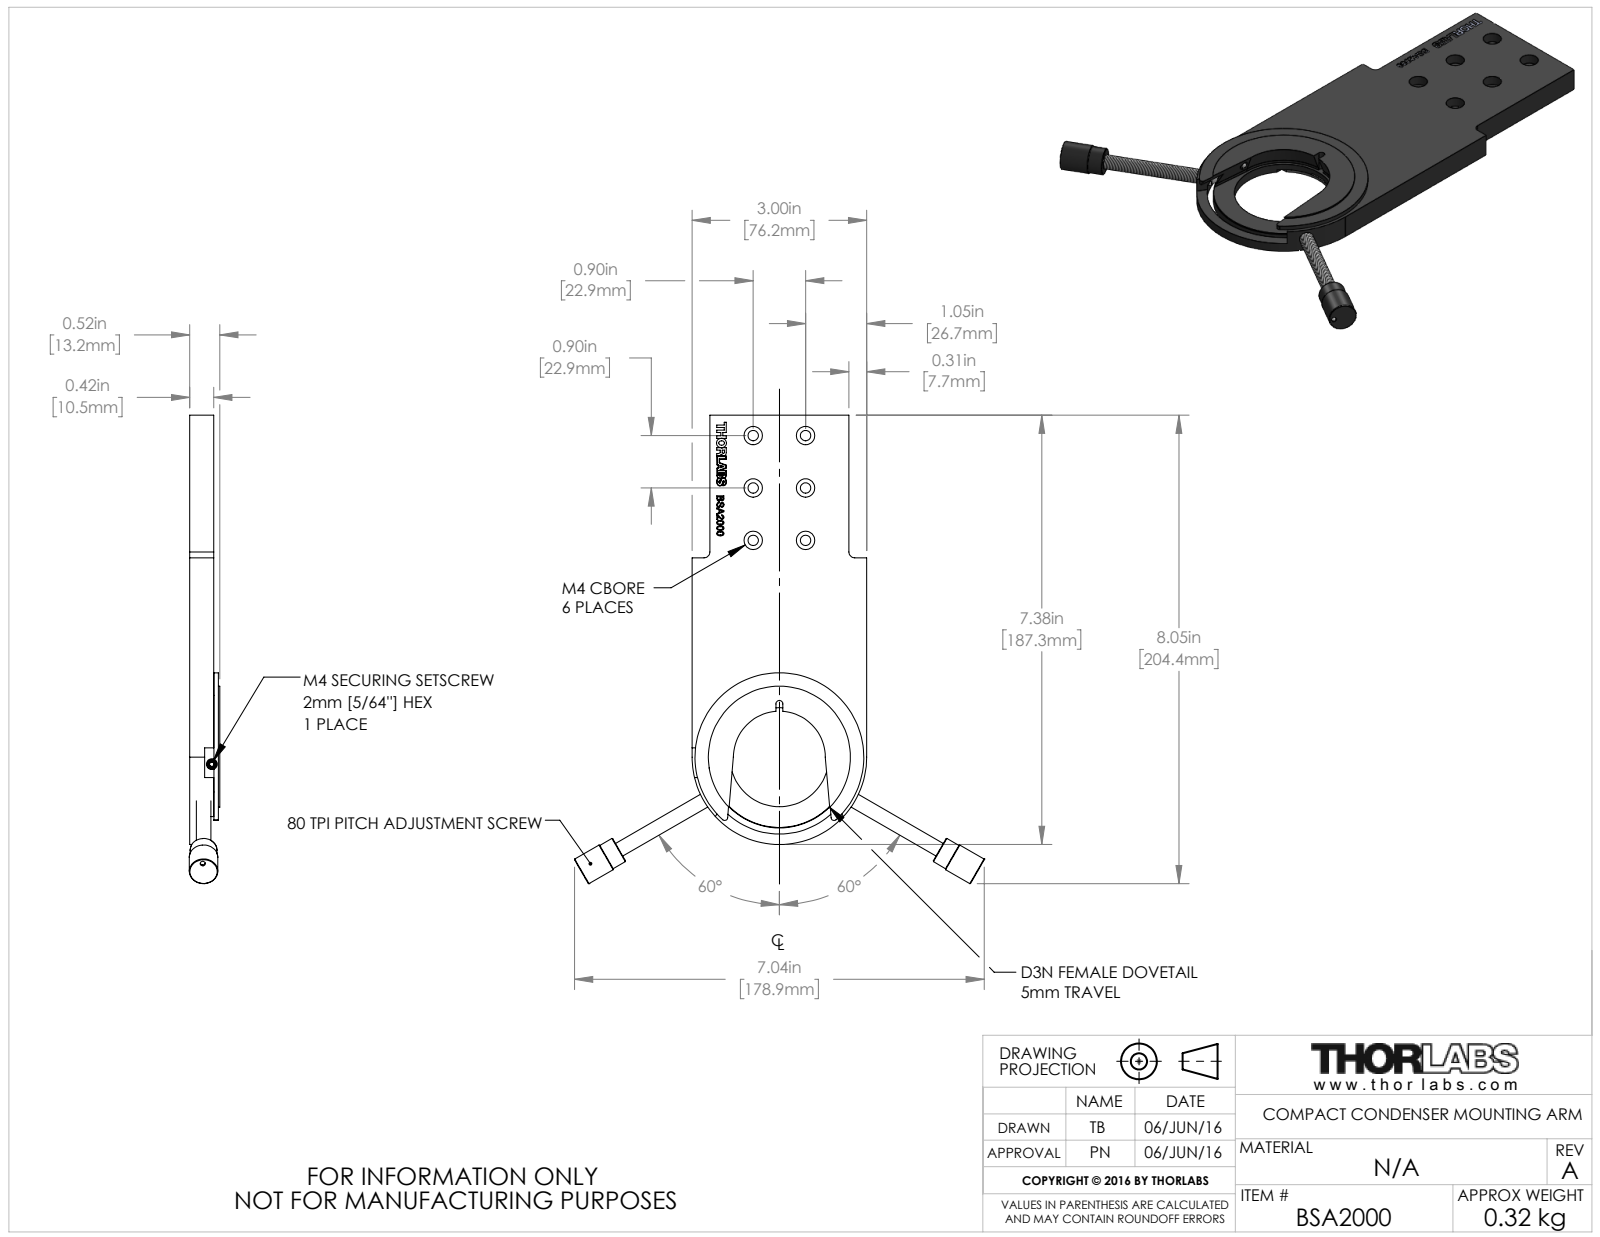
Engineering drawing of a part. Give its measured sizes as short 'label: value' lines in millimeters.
name: TTN030414-E0W
written by: SolidWorks 2016 (AUTOMOTIVE_DESIGN)
unit: mm
bodies: 17 solids, 753 faces (286 planar, 232 cylindrical, 235 other)
size: 204.4 × 178.88 × 13.34
volume: 108 611 mm³; area: 45 212 mm²
holes: 6× ⌀4.5, 6× ⌀8, 2× ⌀2.29, 2× ⌀2.5, 2× ⌀4.78, 2× ⌀5.94, 2× ⌀6.04, 2× ⌀6.3, 1× ⌀2.97, 1× ⌀3.3, 1× ⌀4.7, 1× ⌀43.18
bosses: 3× ⌀3, 2× ⌀12.45, 2× ⌀11.68, 2× ⌀6.35, 2× ⌀6, 2× ⌀2.35, 1× ⌀61.72, 1× ⌀5.97
rounds: 8× R3.05, 3× R0.74, 3× R1.37, 2× R1.27, 2× R1.97, 2× R2.54, 2× R8.89, 2× R30.17
face distances: 10.55, 1.91, 2.03, 4.57, 10.42, 10.54, 4.32, 10.67, 2.54, 7.75
hole spacings: 22.86, 32.33, 4.07, 17.78, 45.72, 51.12, 59.29, 71.1
